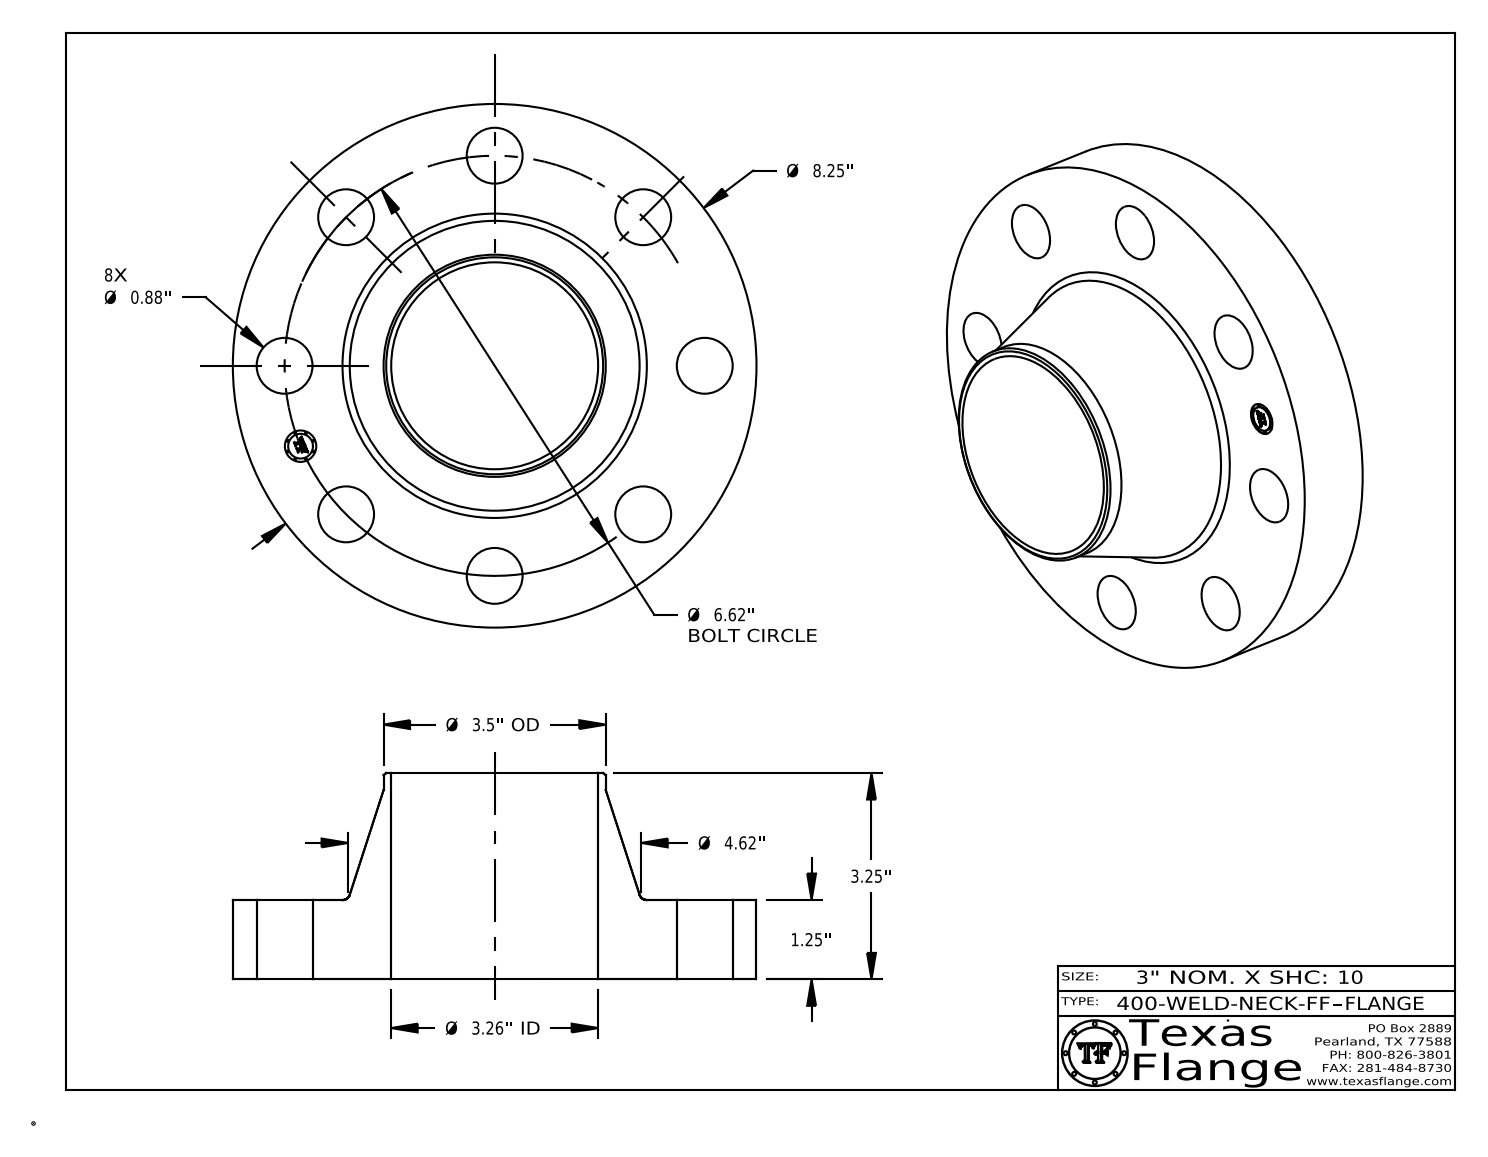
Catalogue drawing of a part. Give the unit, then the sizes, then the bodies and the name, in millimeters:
Units: millimetres
Overall size (bounding box): 209.6 × 209.6 × 82.6
Round holes (diameter × count): ⌀22.4 ×8, ⌀12.6 ×1, ⌀82.8 ×1
Round bosses / shafts (diameter × count): ⌀0.8 ×8, ⌀209.6 ×1, ⌀88.9 ×1, ⌀9.9 ×1
Main face-to-face distances: 31.8, 82.6, 50.8, 0.4, 31.4, 51.2, 3.8, 3.7, 0.7, 2.4
Hole centre spacings: 84.1, 64.3, 155.3, 118.9, 118.9, 32.8, 93.4, 164.9
Volume: 963 100 mm³ · Surface area: 124 100 mm²
Bodies: 1 solid, 416 faces (368 planar, 42 cylindrical, 6 other)
Part name (STEP PRODUCT): 400-WELD-NECK-FF
STEP written by: CATIA V5 STEP AP214 (AUTOMOTIVE_DESIGN)
